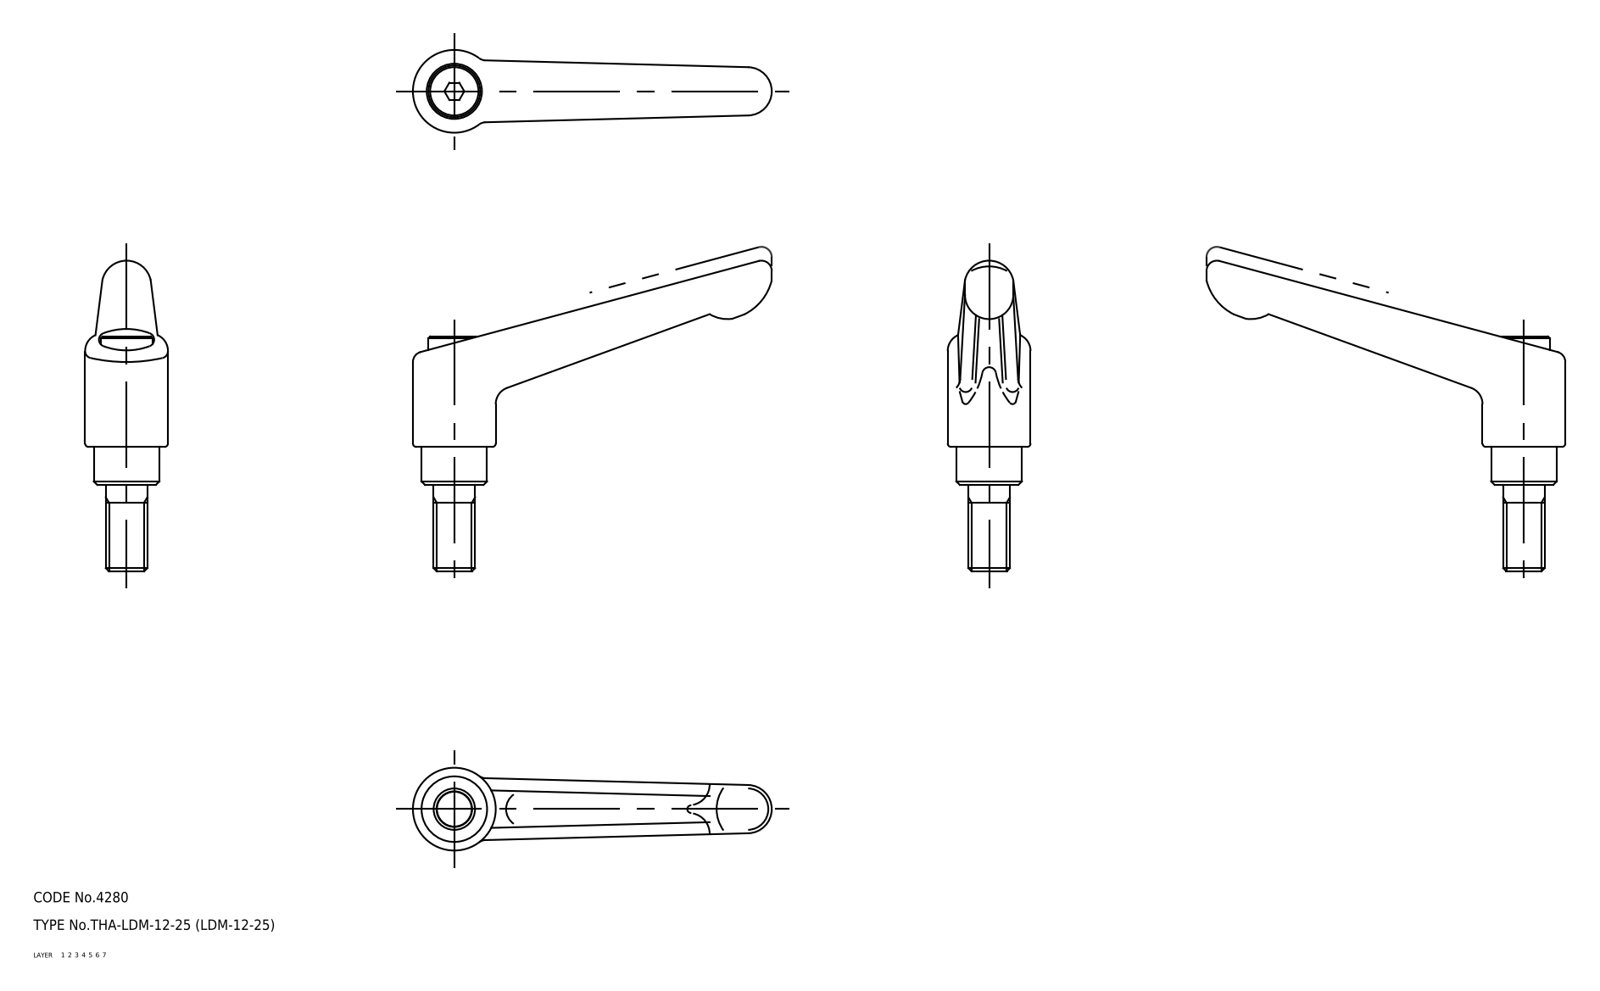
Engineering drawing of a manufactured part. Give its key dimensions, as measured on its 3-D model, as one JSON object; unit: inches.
{"part_name": "sleeve; screw; handle; LDM_12_25_11739_36", "step_written_by": "CADfix (AUTOMOTIVE_DESIGN)", "units": "inches", "bodies": {"solids": 3, "faces": 96, "planar": 0, "cylindrical": 0, "other": 96}, "overall_size": [4.094, 3.543, 0.945], "volume_in3": 1.883, "surface_area_in2": 20.41}
